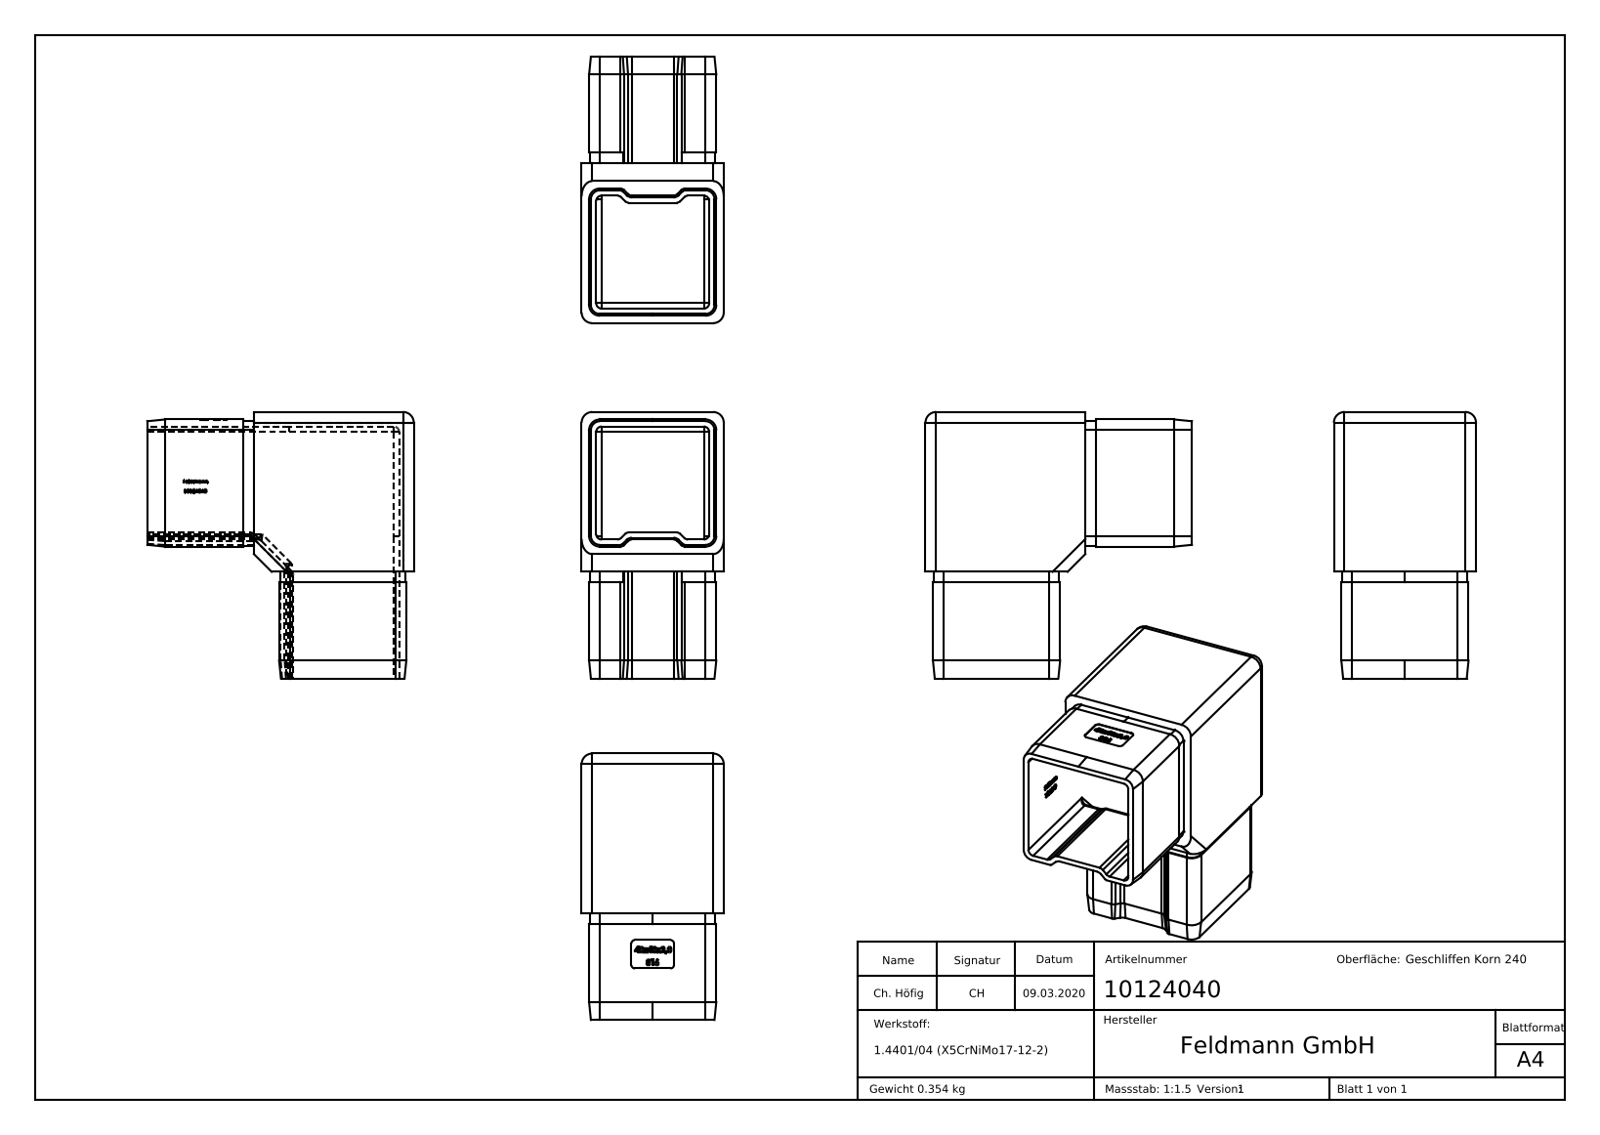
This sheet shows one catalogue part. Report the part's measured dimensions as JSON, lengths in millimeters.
{"part_name": "10124040", "step_written_by": "SolidWorks 2015 (CONFIG_CONTROL_DESIGN)", "units": "millimeters", "bodies": {"solids": 1, "faces": 548, "planar": 310, "cylindrical": 68, "other": 170}, "overall_size": [75, 75, 40], "volume_mm3": 44273, "surface_area_mm2": 30925, "partial_cylinders_radius": [[1.5, 35], [3, 15], [2.7, 8], [1, 4]], "face_to_face_distances": [4.1, 2, 31.8, 35.9, 33.8, 2.1, 37.9, 35.8, 40, 33.9]}
